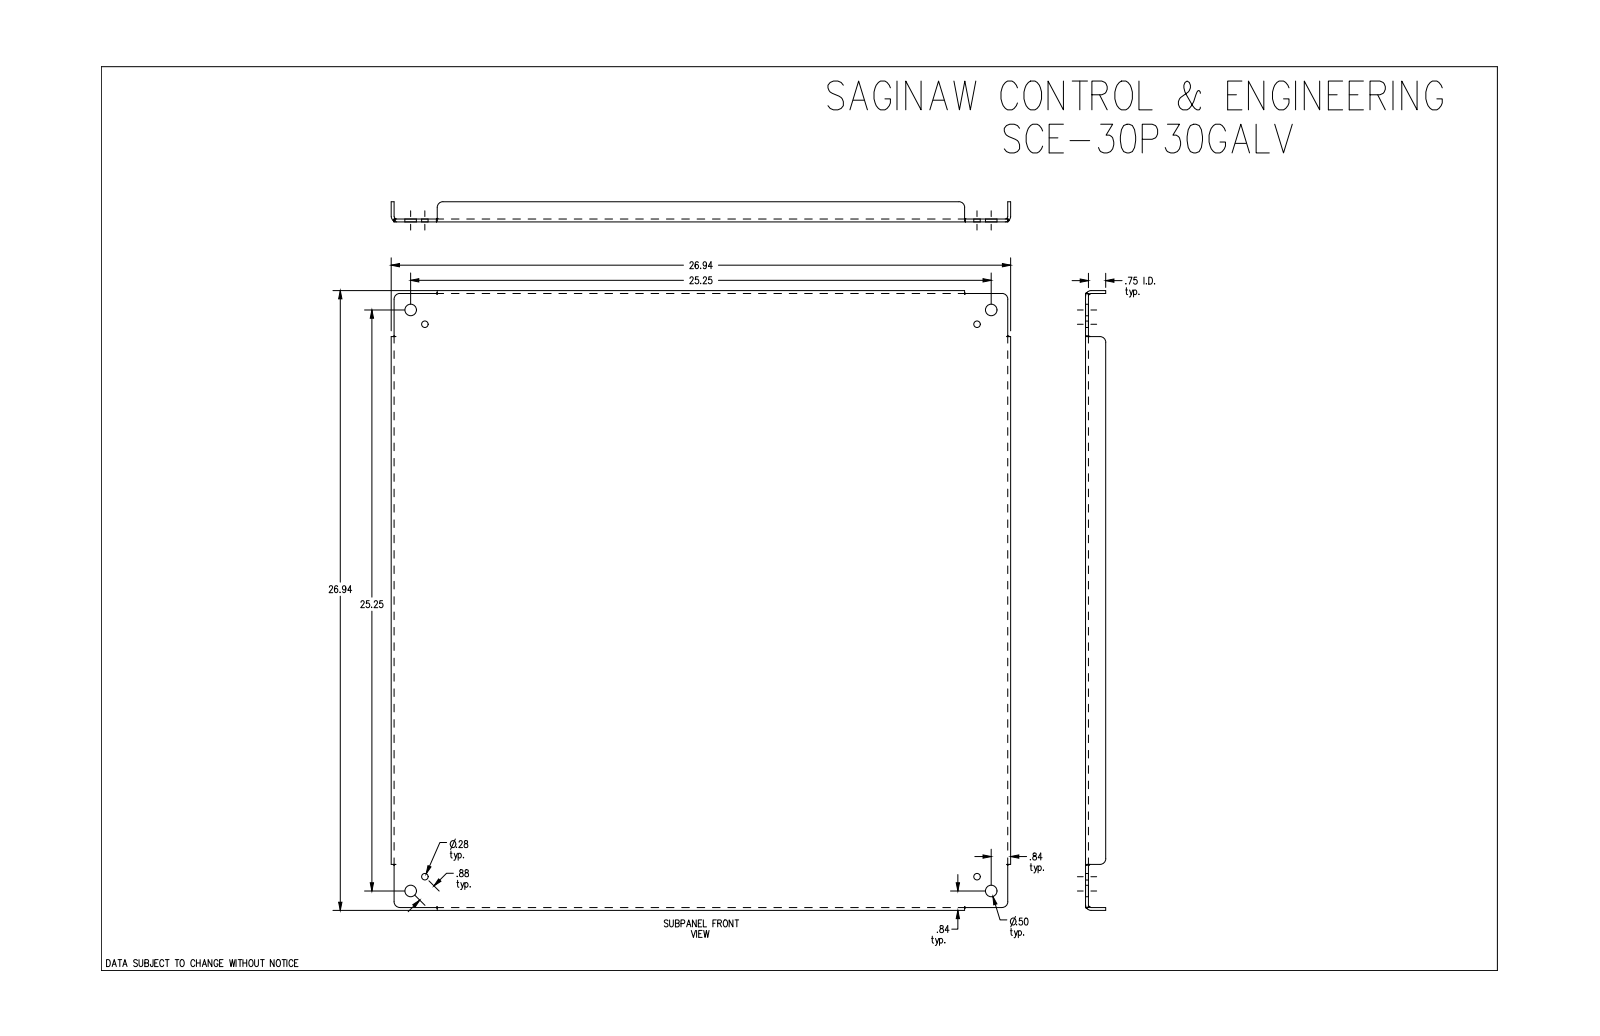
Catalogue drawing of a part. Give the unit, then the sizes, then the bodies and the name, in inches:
Units: inches
Overall size (bounding box): 26.938 × 26.938 × 0.875
Round holes (diameter × count): ⌀0.281 ×4, ⌀0.5 ×4
Partial cylindrical surfaces — rounded edges, fillets, slot ends (radius × count): R0.25 ×8, R0.112 ×4, R0.237 ×4
Main face-to-face distances: 0.125, 0.125, 26.813, 26.687, 26.938, 0.75, 0.875, 2, 24.938, 1.875
Hole centre spacings: 24.639, 0.875, 24.013, 25.25, 34.833, 33.959, 35.708
Volume: 98.05 in³ · Surface area: 1 584 in²
Bodies: 1 solid, 82 faces (30 planar, 28 cylindrical, 24 other)
Part name (STEP PRODUCT): SCE-30P30GALV
STEP written by: SolidWorks 2019 (CONFIG_CONTROL_DESIGN)
